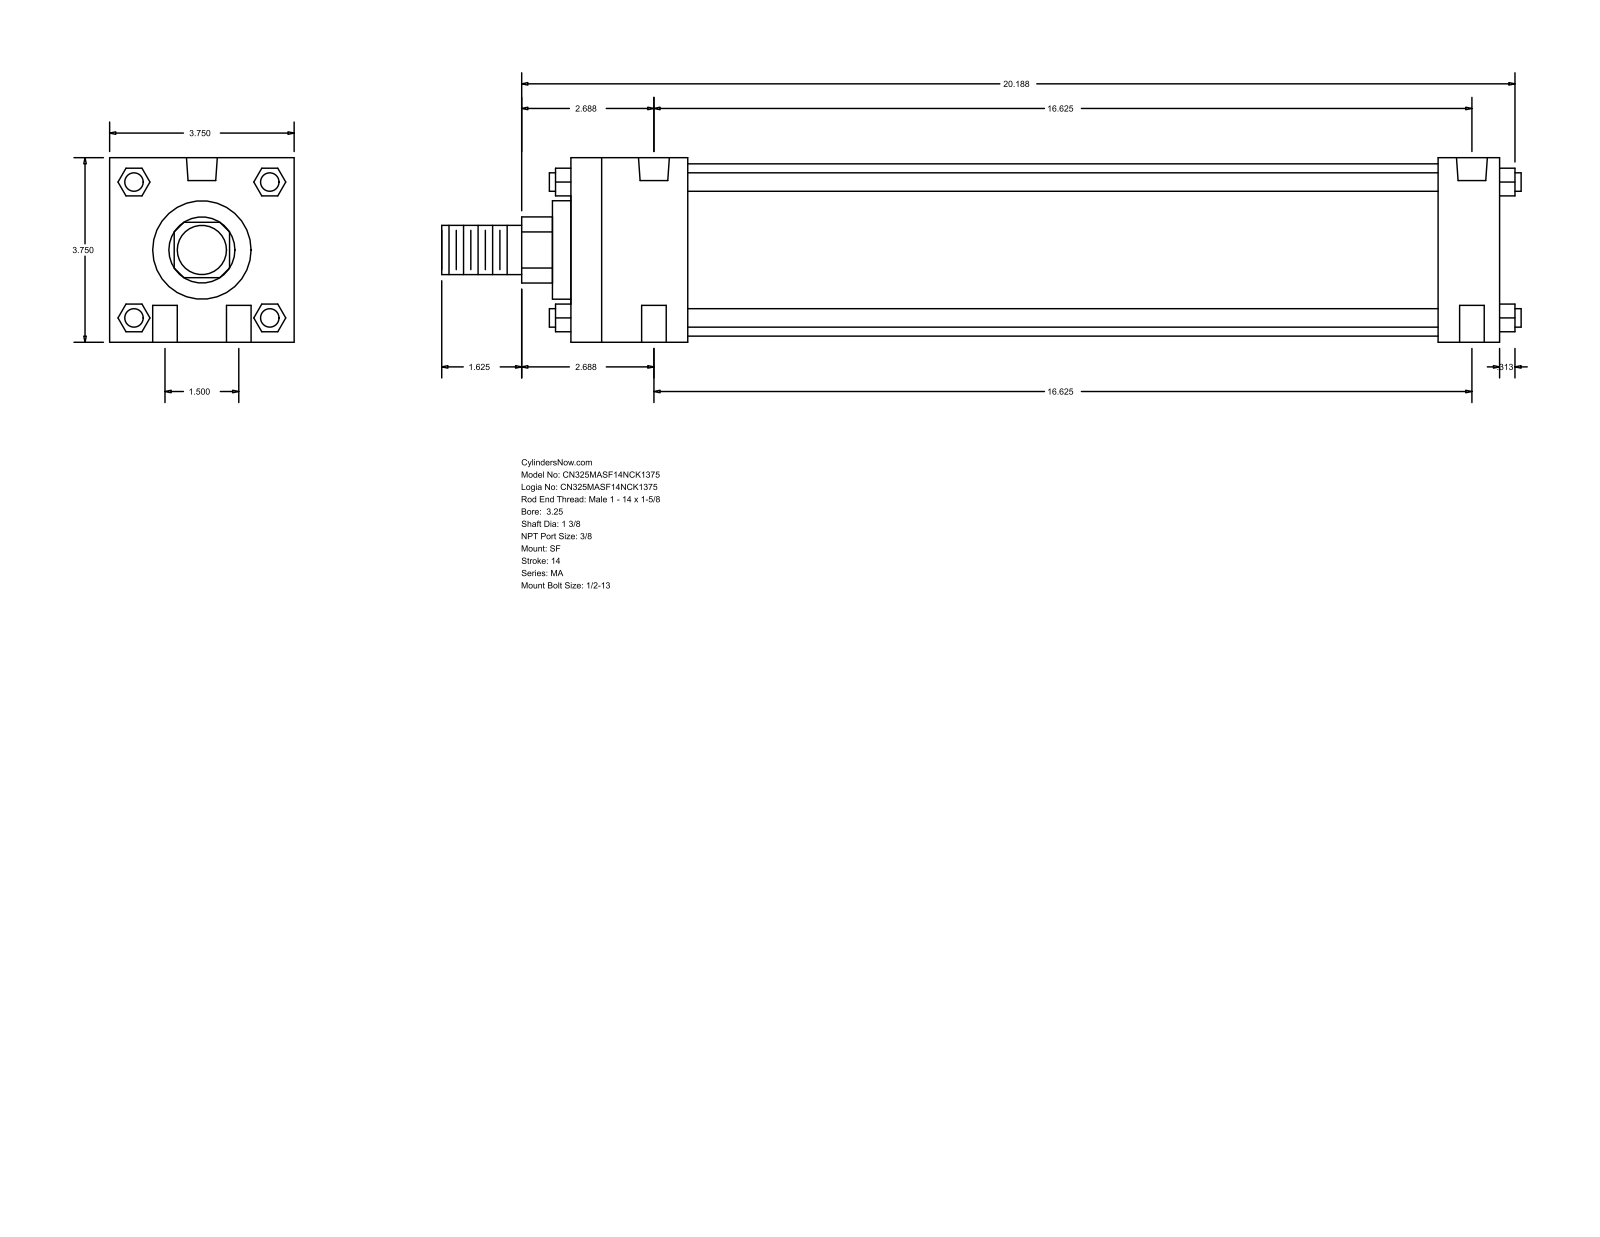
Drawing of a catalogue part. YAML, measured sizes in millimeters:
part_name: "MA_SF__0325_1.375"
step_written_by: "GSSL Pune (CONFIG_CONTROL_DESIGN)"
units: millimeters
bodies: {solids: 0, faces: 124, planar: 94, cylindrical: 30, other: 0}
overall_size: [557.21, 95.25, 95.25]
round_holes:
  - {diameter: 12.7, count: 4}
  - {diameter: 11.11, count: 2}
  - {diameter: 15.93, count: 2}
round_bosses_or_shafts:
  - {diameter: 9.53, count: 4}
  - {diameter: 88.9, count: 1}
  - {diameter: 50.8, count: 1}
  - {diameter: 34.92, count: 1}
  - {diameter: 25.4, count: 1}
partial_cylinders:
  - {radius: 17.06, count: 1}
face_to_face_distances: [95.24, 479.42, 447.67, 31.75, 60.32, 387.35, 419.1, 9.52, 69.84, 457.19]
hole_center_spacings: [19.05, 422.71, 422.28, 38.1, 424, 412.74]
